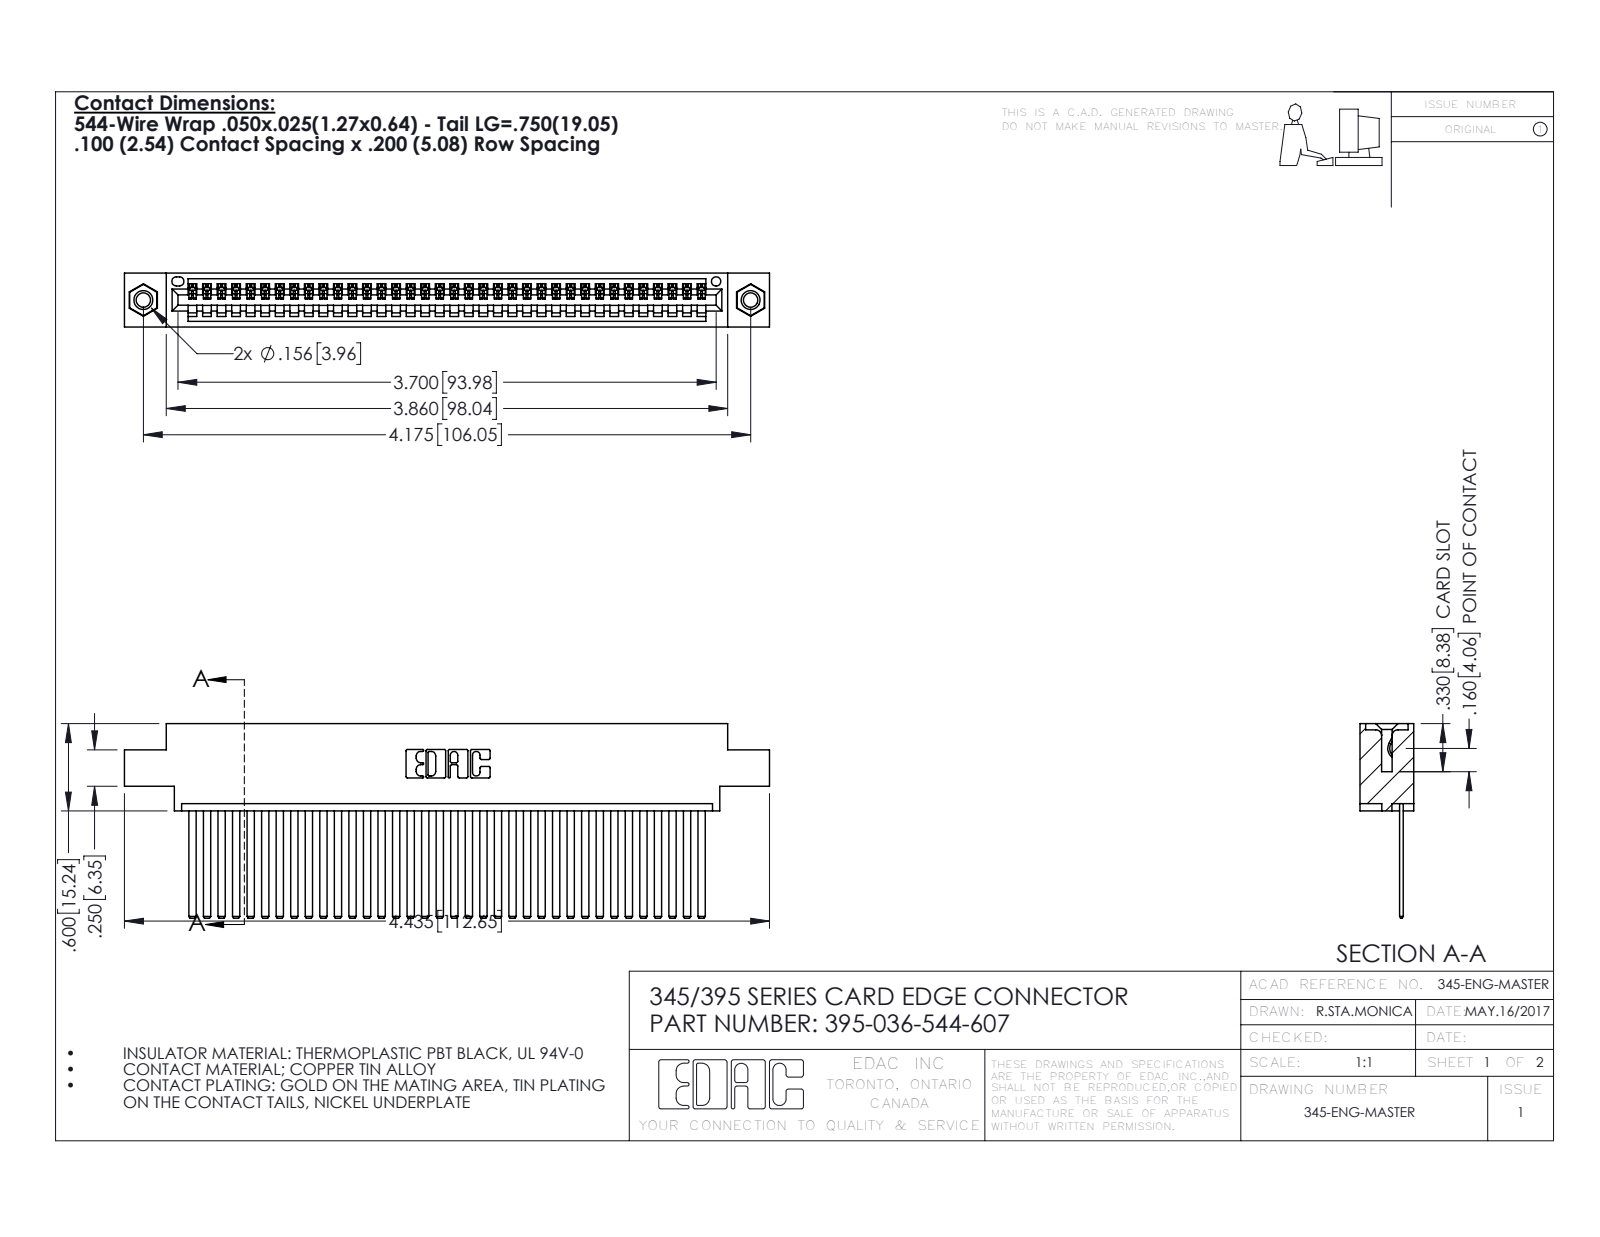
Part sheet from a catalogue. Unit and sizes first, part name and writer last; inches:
Units: inches
Overall size (bounding box): 4.435 × 1.337 × 0.37
Round holes (diameter × count): ⌀0.098 ×2, ⌀0.125 ×2, ⌀0.156 ×2, ⌀0.064 ×1
Round bosses / shafts (diameter × count): ⌀0.155 ×2
Partial cylindrical surfaces — rounded edges, fillets, slot ends (radius × count): R0.006 ×72, R0.01 ×22, R0.007 ×6, R0.031 ×6, R0.026 ×3, R0.031 ×2, R0.04 ×2, R0.014 ×1
Main face-to-face distances: 0.072, 0.298, 0.025, 0.098, 0.272, 0.37, 0.2, 0.225, 0.175, 0.149
Hole centre spacings: 0.27, 3.939, 4.175
Volume: 0.668 in³ · Surface area: 24.6 in²
Bodies: 39 solids, 2062 faces (1412 planar, 634 cylindrical, 16 other)
Part name (STEP PRODUCT): 345-292-001_345-293-144; 345-250-001_345-250-005-103; 345 Part_0.170 Offset - 0.156 Dia-TI; 395-036-544-607
STEP written by: SolidWorks 2016 (CONFIG_CONTROL_DESIGN)
